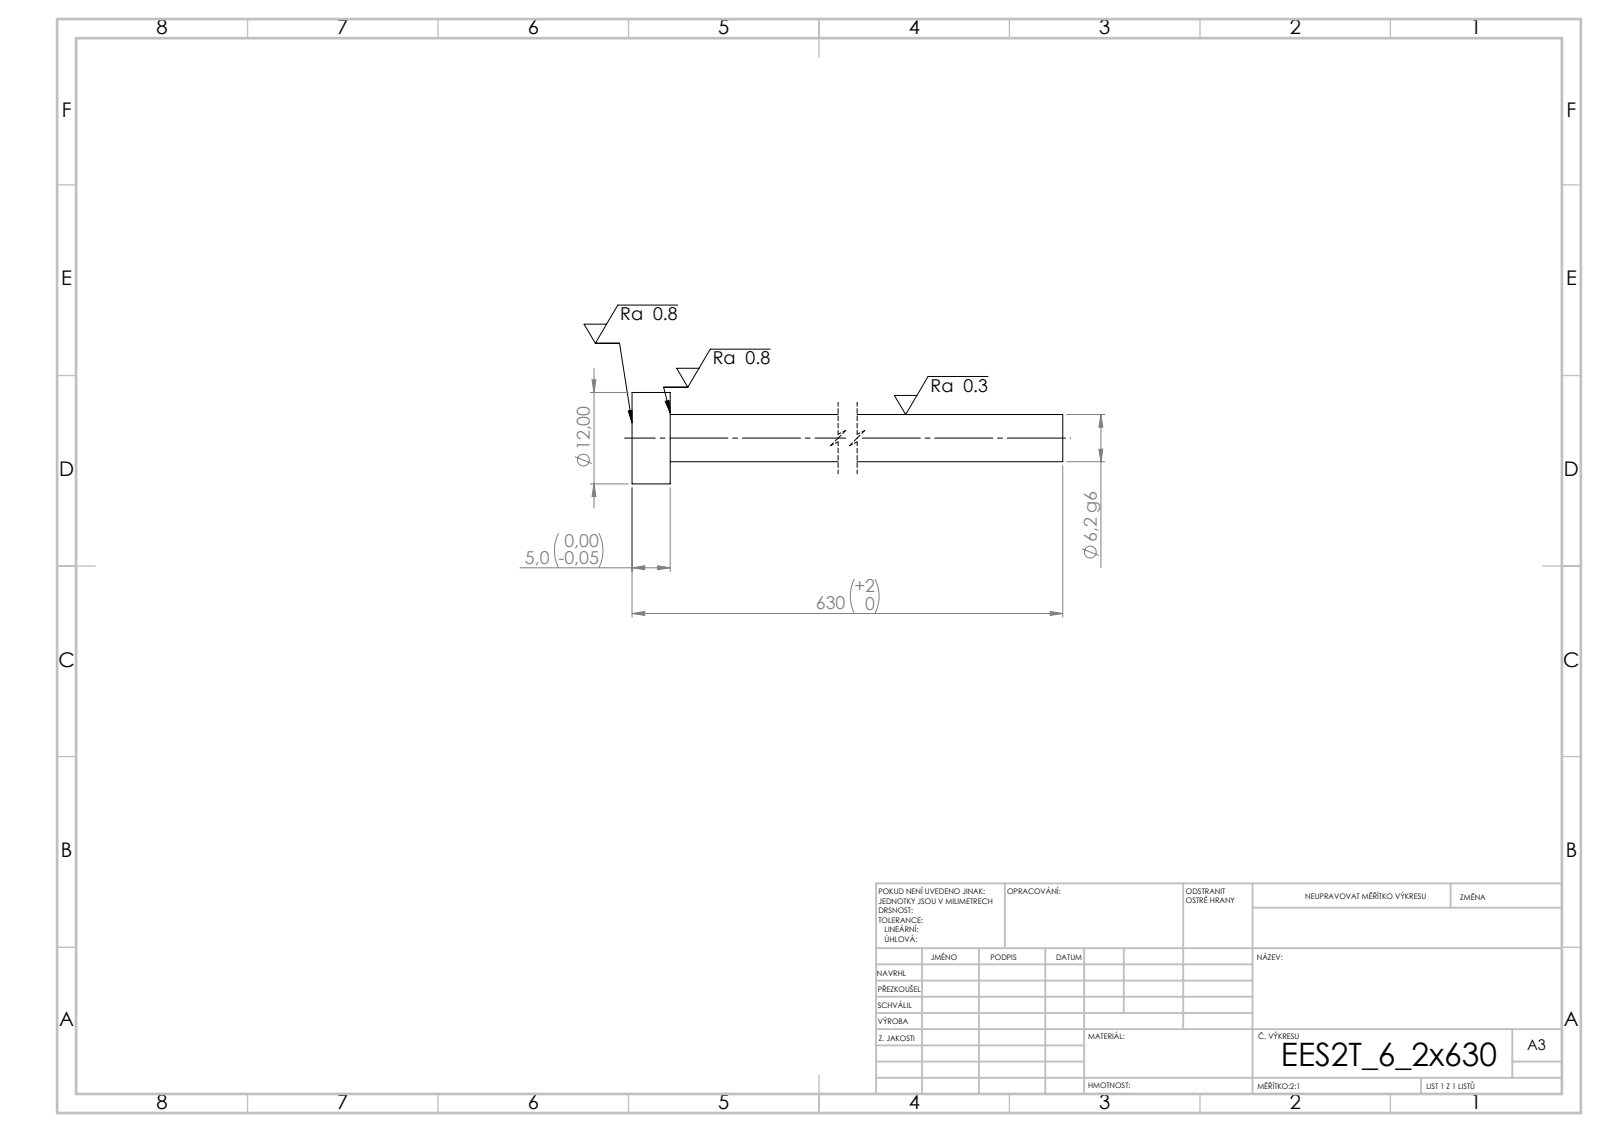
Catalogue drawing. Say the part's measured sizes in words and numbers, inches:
Its 3-D file was written by "SolidWorks 2019 (CONFIG_CONTROL_DESIGN)". It is 1 solid with 7 faces: 3 planar, 4 cylindrical and 0 other. Overall it measures 24.803 by 0.472 by 0.472 inches. Its volume is 1.186 cubic inches and its surface area 19.51 square inches. Round bosses or shafts: 1 of diameter 0.472, 1 of diameter 0.244. The main face-to-face distances are 0.197, 24.803, 24.606.
